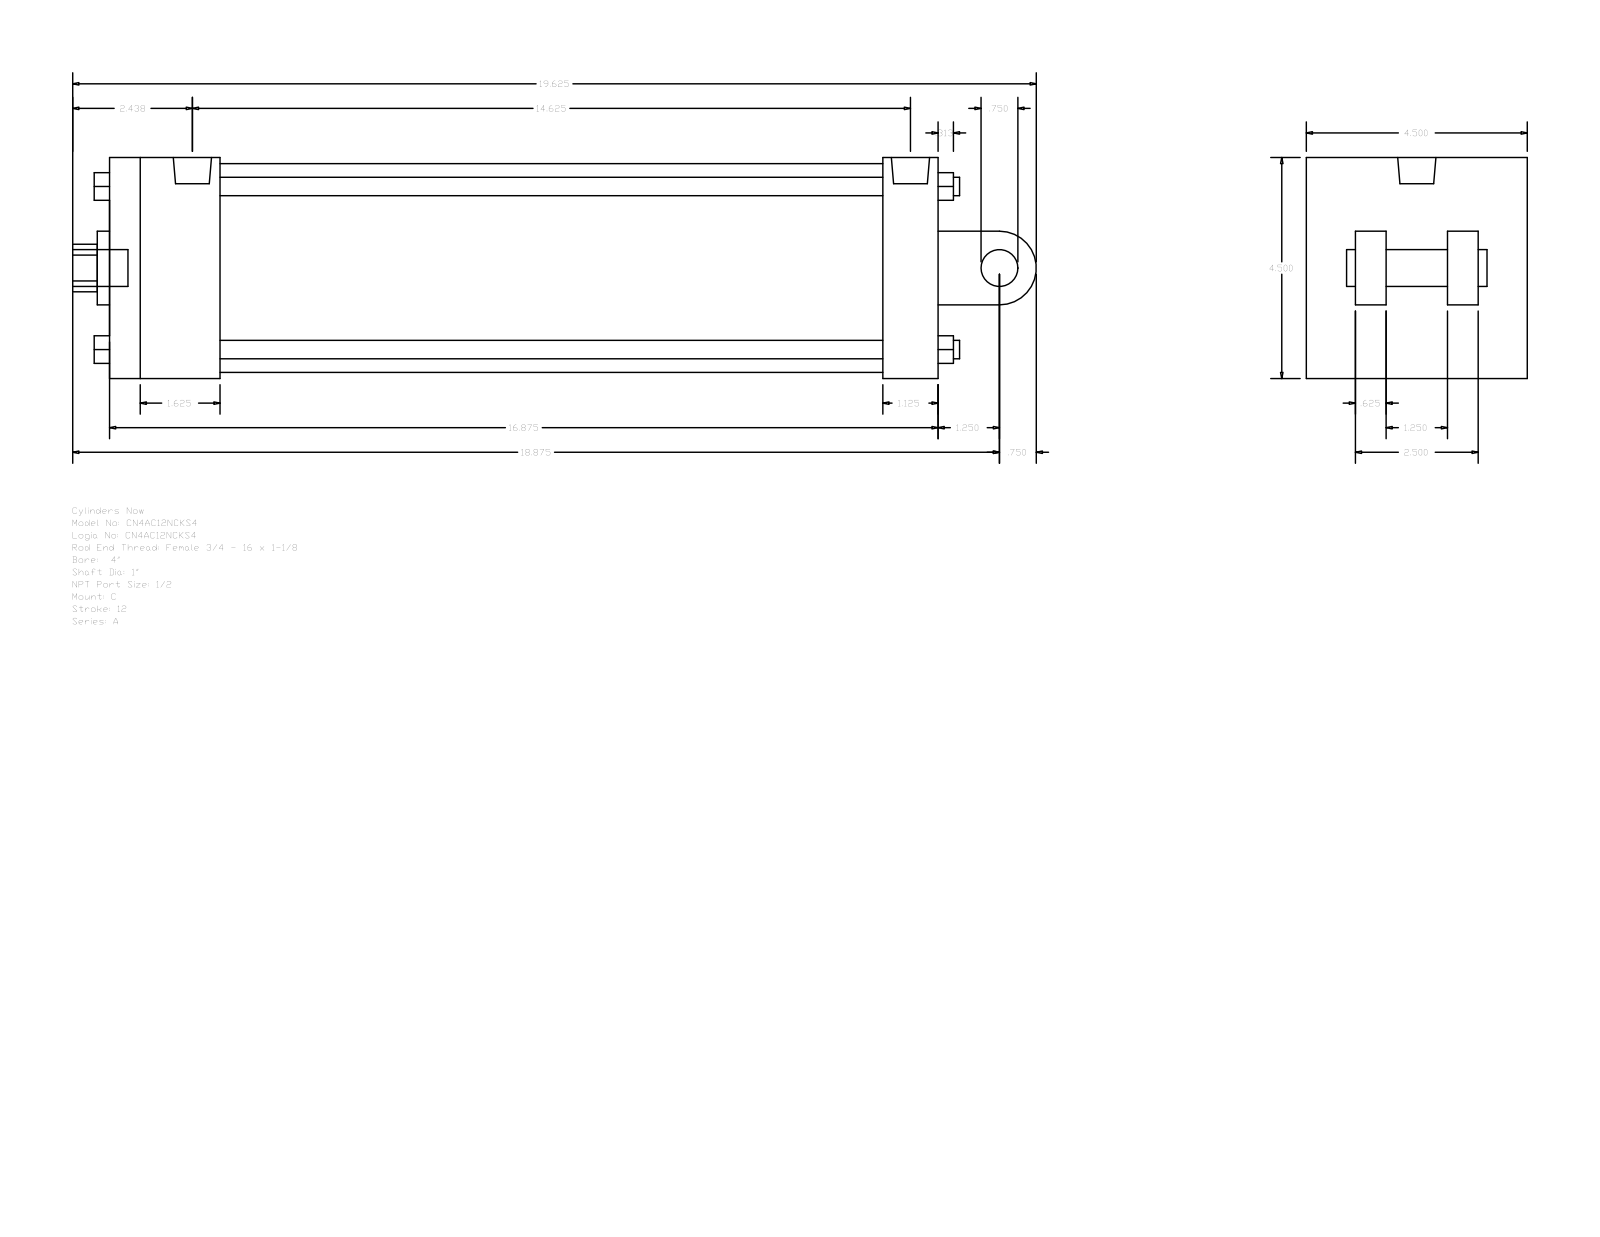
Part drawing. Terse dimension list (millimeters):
name: A_C__0400_1
written by: GSSL Pune (CONFIG_CONTROL_DESIGN)
unit: mm
bodies: 0 solids, 135 faces (102 planar, 33 cylindrical, 0 other)
size: 498.48 × 114.3 × 114.3
holes: 2× ⌀8.73, 1× ⌀19.77, 1× ⌀25.4, 1× ⌀38.1, 1× ⌀107.95
bosses: 4× ⌀9.53, 2× ⌀19.05, 2× ⌀8.73, 1× ⌀19.77
rounds: 1× R12.29, 1× R19.05
face distances: 114.3, 428.63, 73.03, 400.05, 28.58, 57.15, 342.9, 371.48, 15.87, 47.63
hole spacings: 3.18
